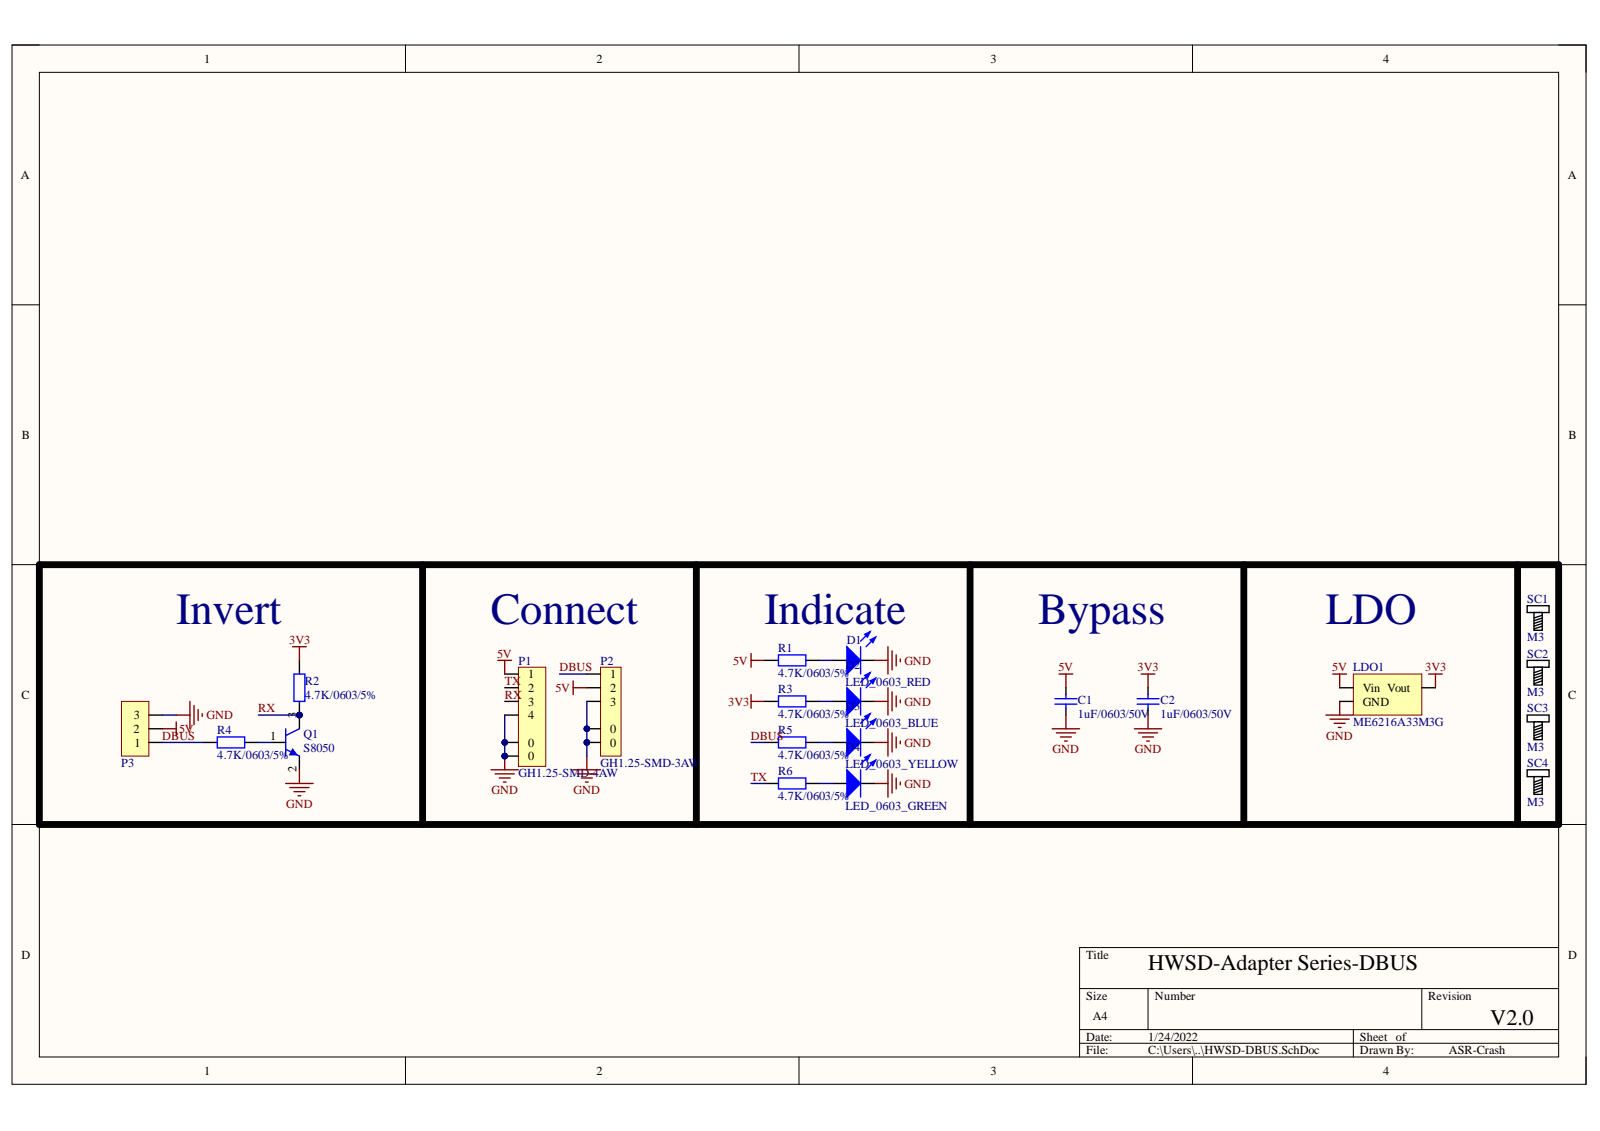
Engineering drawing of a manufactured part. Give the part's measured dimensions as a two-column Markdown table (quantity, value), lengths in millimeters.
| quantity | value |
| --- | --- |
| part name | PCB; Board; R6; 6513774352 (+6 more) |
| STEP written by | Open CASCADE 6.8 (AUTOMOTIVE_DESIGN) |
| units | millimeters |
| bodies | 30 solids, 1081 faces (849 planar, 122 cylindrical, 110 other) |
| overall size | 20.04 × 20 × 10.18 |
| volume | 854 mm³ |
| surface area | 1 762 mm² |
| round holes (diameter × count) | 3 × 4, 1 × 3 |
| partial cylindrical surfaces (radius × count) | 0.1 × 8, 0.15 × 8, 0.25 × 8, 2.54 × 4, 0.64 × 1 |
| main face-to-face distances | 1.69, 2.54, 4.25, 5.94, 0.64, 3.84, 20, 0.95, 1, 0.6 |
| hole center spacings | 8.94, 10.55, 12.48, 14.92, 2.54, 21.1, 5.08 |
